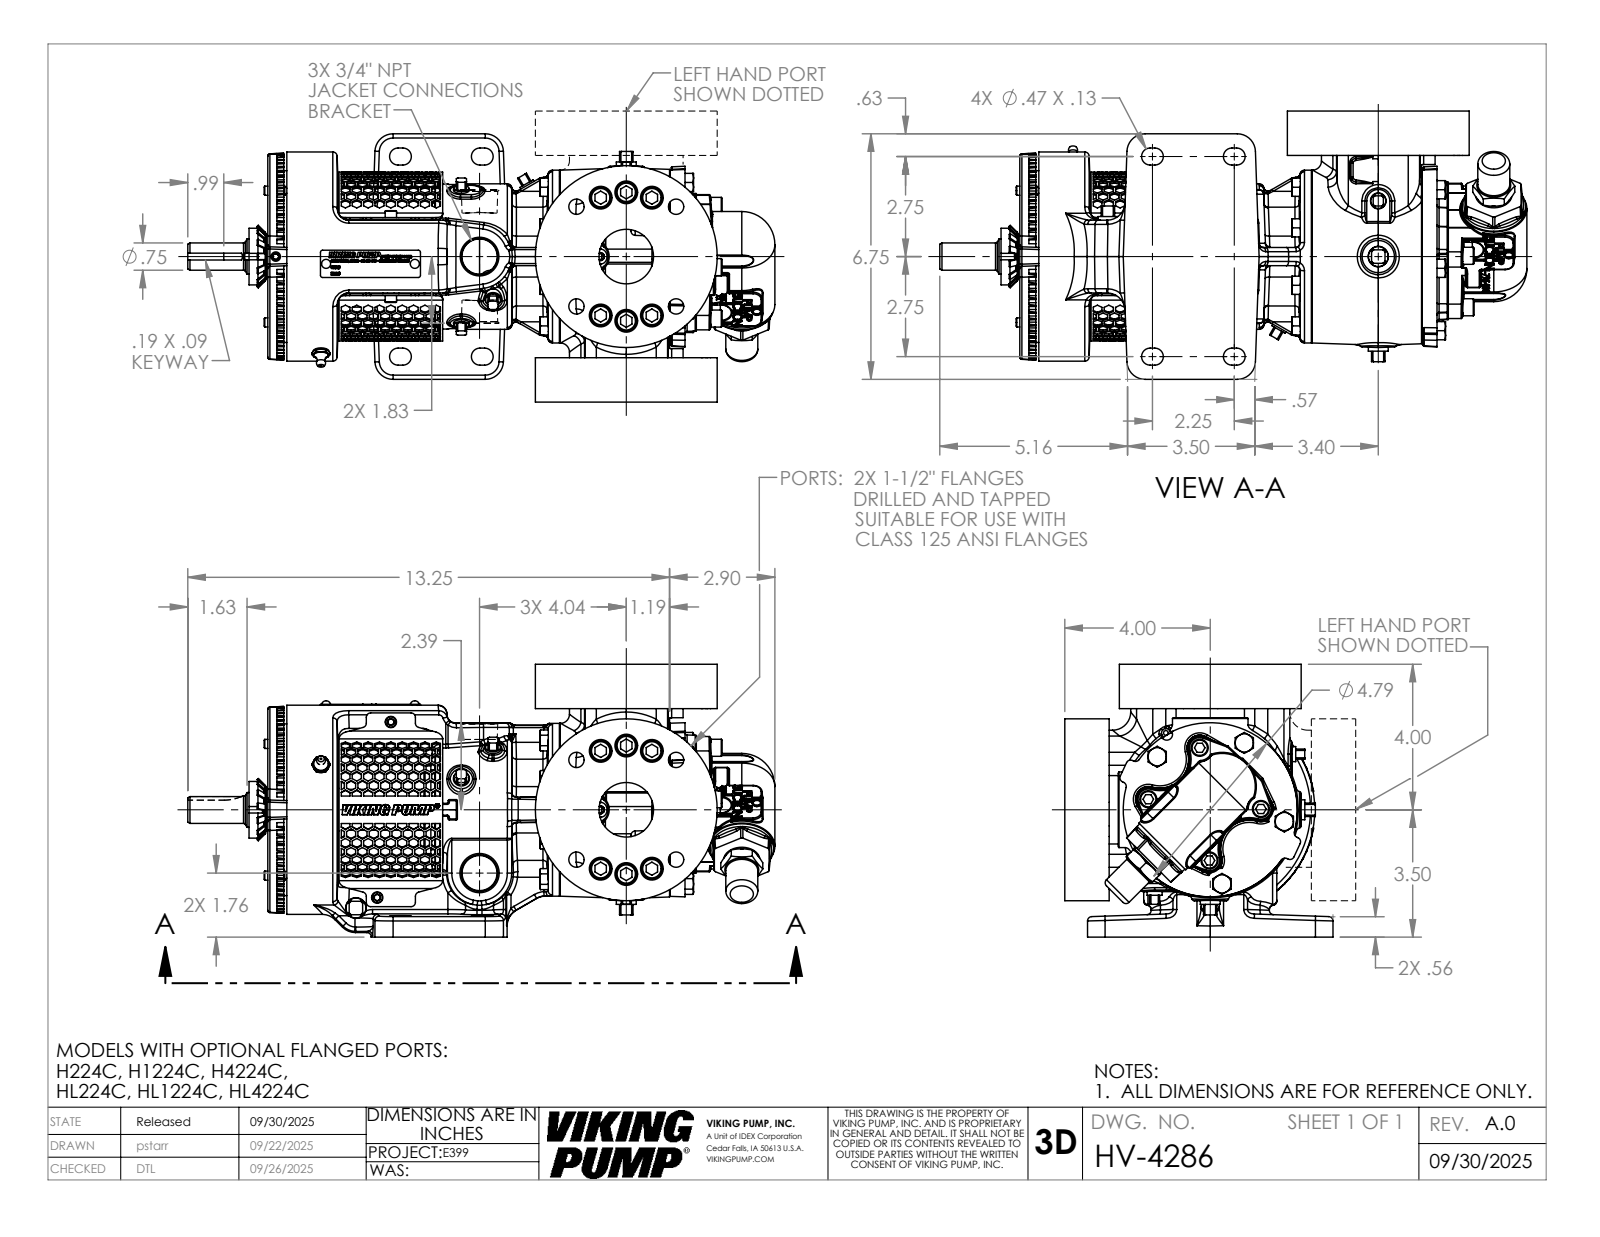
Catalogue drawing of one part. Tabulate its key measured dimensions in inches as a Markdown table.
| quantity | value |
| --- | --- |
| part name | HV-4286 |
| STEP written by | SolidWorks 2024 (AUTOMOTIVE_DESIGN) |
| units | inches |
| bodies | 1 solid, 5249 faces (1877 planar, 1010 cylindrical, 2362 other) |
| overall size | 16.145 × 7.5 × 7.375 |
| volume | 254.8 in³ |
| surface area | 648.4 in² |
| round holes (diameter × count) | 0.25 × 9, 0.625 × 9, 0.422 × 8, 0.34 × 4, 0.344 × 4, 0.159 × 3, 0.197 × 3, 0.625 × 3, 0.257 × 2, 1.5 × 2, 0.986 × 1, 0.989 × 1 |
| round bosses / shafts (diameter × count) | 0.563 × 12, 0.469 × 4, 0.313 × 4, 0.312 × 3, 0.19 × 3, 5 × 2, 0.25 × 2, 5.75 × 1 |
| partial cylindrical surfaces (radius × count) | 0.054 × 140, 0.03 × 94, 0.12 × 85, 0.06 × 56, 0.5 × 40, 0.25 × 10, 0.234 × 8, 0.38 × 8 |
| main face-to-face distances | 1.22, 7.5, 1.94, 11.474, 9.533, 6.28, 1.5, 0.524, 1.417, 10.95 |
| hole center spacings | 1.766, 2.56, 0.711, 0.719, 1.426, 1.937, 2.089, 2.74 |
